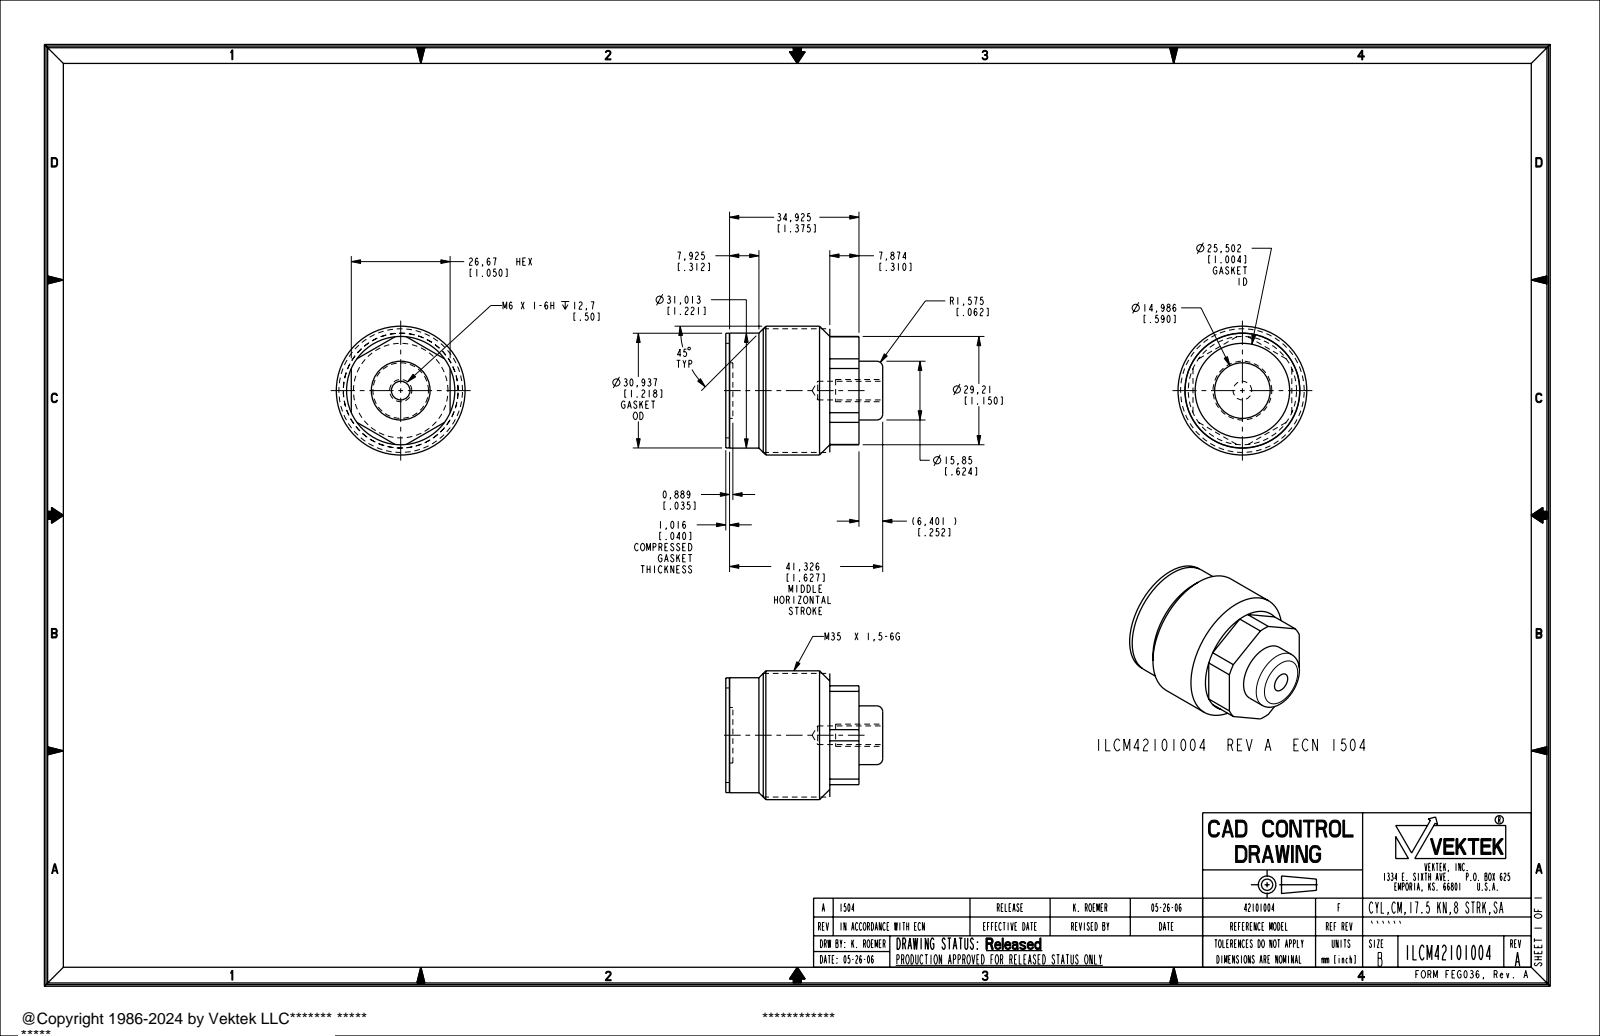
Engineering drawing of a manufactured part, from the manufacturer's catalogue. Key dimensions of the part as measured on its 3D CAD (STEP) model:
Part name (STEP PRODUCT): ILCM42101004
STEP written by: PRO/ENGINEER BY PARAMETRIC TECHNOLOGY CORPORATION, 2004290 (AUTOMOTIVE_DESIGN_CC2)
Units: millimetres
Bodies: 2 solids, 52 faces (20 planar, 24 cylindrical, 8 other)
Overall size (bounding box): 42.34 × 34.75 × 34.75
Volume: 29 300 mm³ · Surface area: 9 418 mm²
Round holes (diameter × count): ⌀5.03 ×1, ⌀14.99 ×1, ⌀25.5 ×1
Round bosses / shafts (diameter × count): ⌀34.75 ×1, ⌀33.35 ×1, ⌀31.01 ×1, ⌀30.94 ×1, ⌀15.85 ×1, ⌀5.99 ×1
Partial cylindrical surfaces — rounded edges, fillets, slot ends (radius × count): R14.61 ×1
Main face-to-face distances: 27.05, 34.92, 7.87, 0.99, 1.02, 28.07, 35.94, 27.08, 34.95, 26.66
